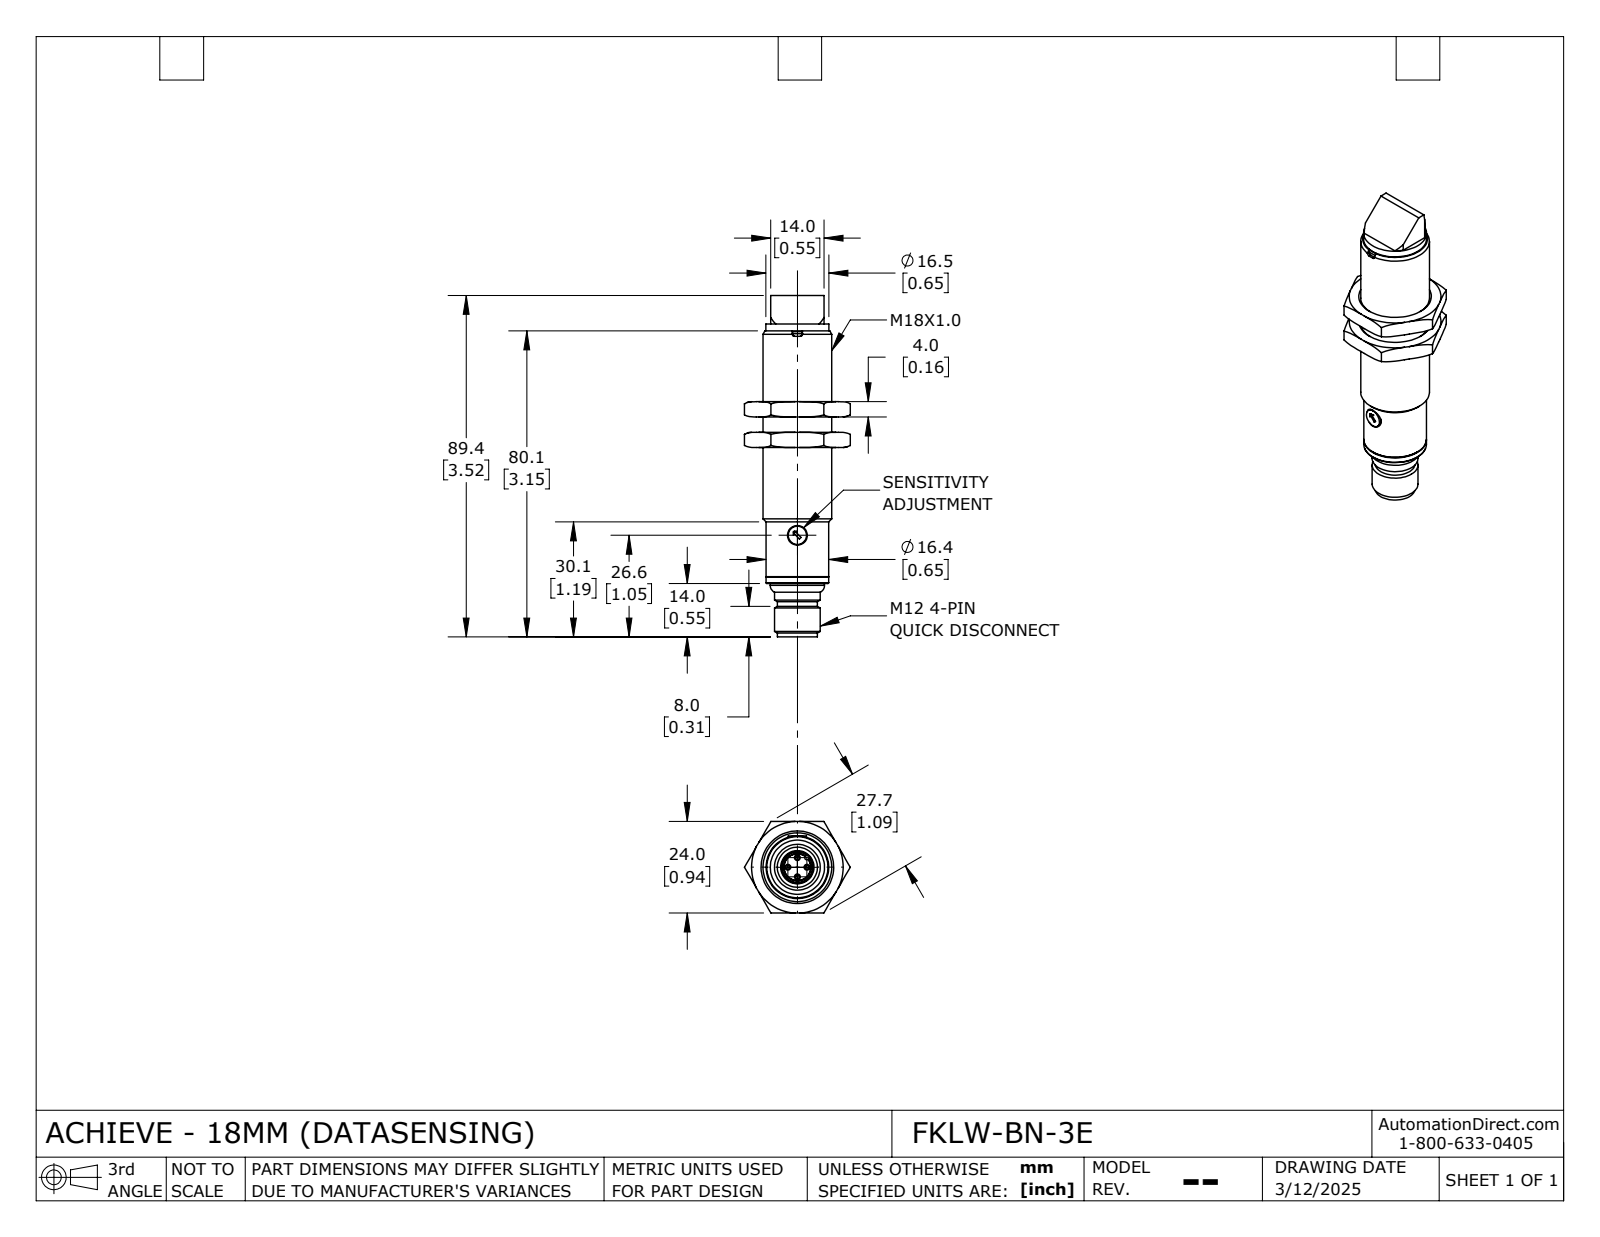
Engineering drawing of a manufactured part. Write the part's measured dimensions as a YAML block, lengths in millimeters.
part_name: "FKLW-BN-3E_Default"
step_written_by: "SolidWorks 2024 (CONFIG_CONTROL_DESIGN)"
units: millimeters
bodies: {solids: 4, faces: 155, planar: 67, cylindrical: 35, other: 53}
overall_size: [89.4, 27.7, 24]
volume: 20170
surface_area: 8800
round_holes:
  - {diameter: 2.7, count: 1}
  - {diameter: 4.7, count: 1}
  - {diameter: 7.1, count: 1}
  - {diameter: 8.3, count: 1}
  - {diameter: 15, count: 1}
  - {diameter: 15.8, count: 1}
  - {diameter: 18, count: 1}
round_bosses_or_shafts:
  - {diameter: 1, count: 4}
  - {diameter: 16.5, count: 1}
  - {diameter: 16.4, count: 1}
  - {diameter: 14.2, count: 1}
  - {diameter: 12, count: 1}
  - {diameter: 10.5, count: 1}
  - {diameter: 7, count: 1}
  - {diameter: 4.8, count: 1}
partial_cylinders:
  - {radius: 0.5, count: 4}
  - {radius: 0.6, count: 1}
  - {radius: 8.1, count: 1}
  - {radius: 8.4, count: 1}
face_to_face_distances: [4, 8, 24, 12, 2.9, 0.4, 3.3, 2.8, 2.4, 0.5]
